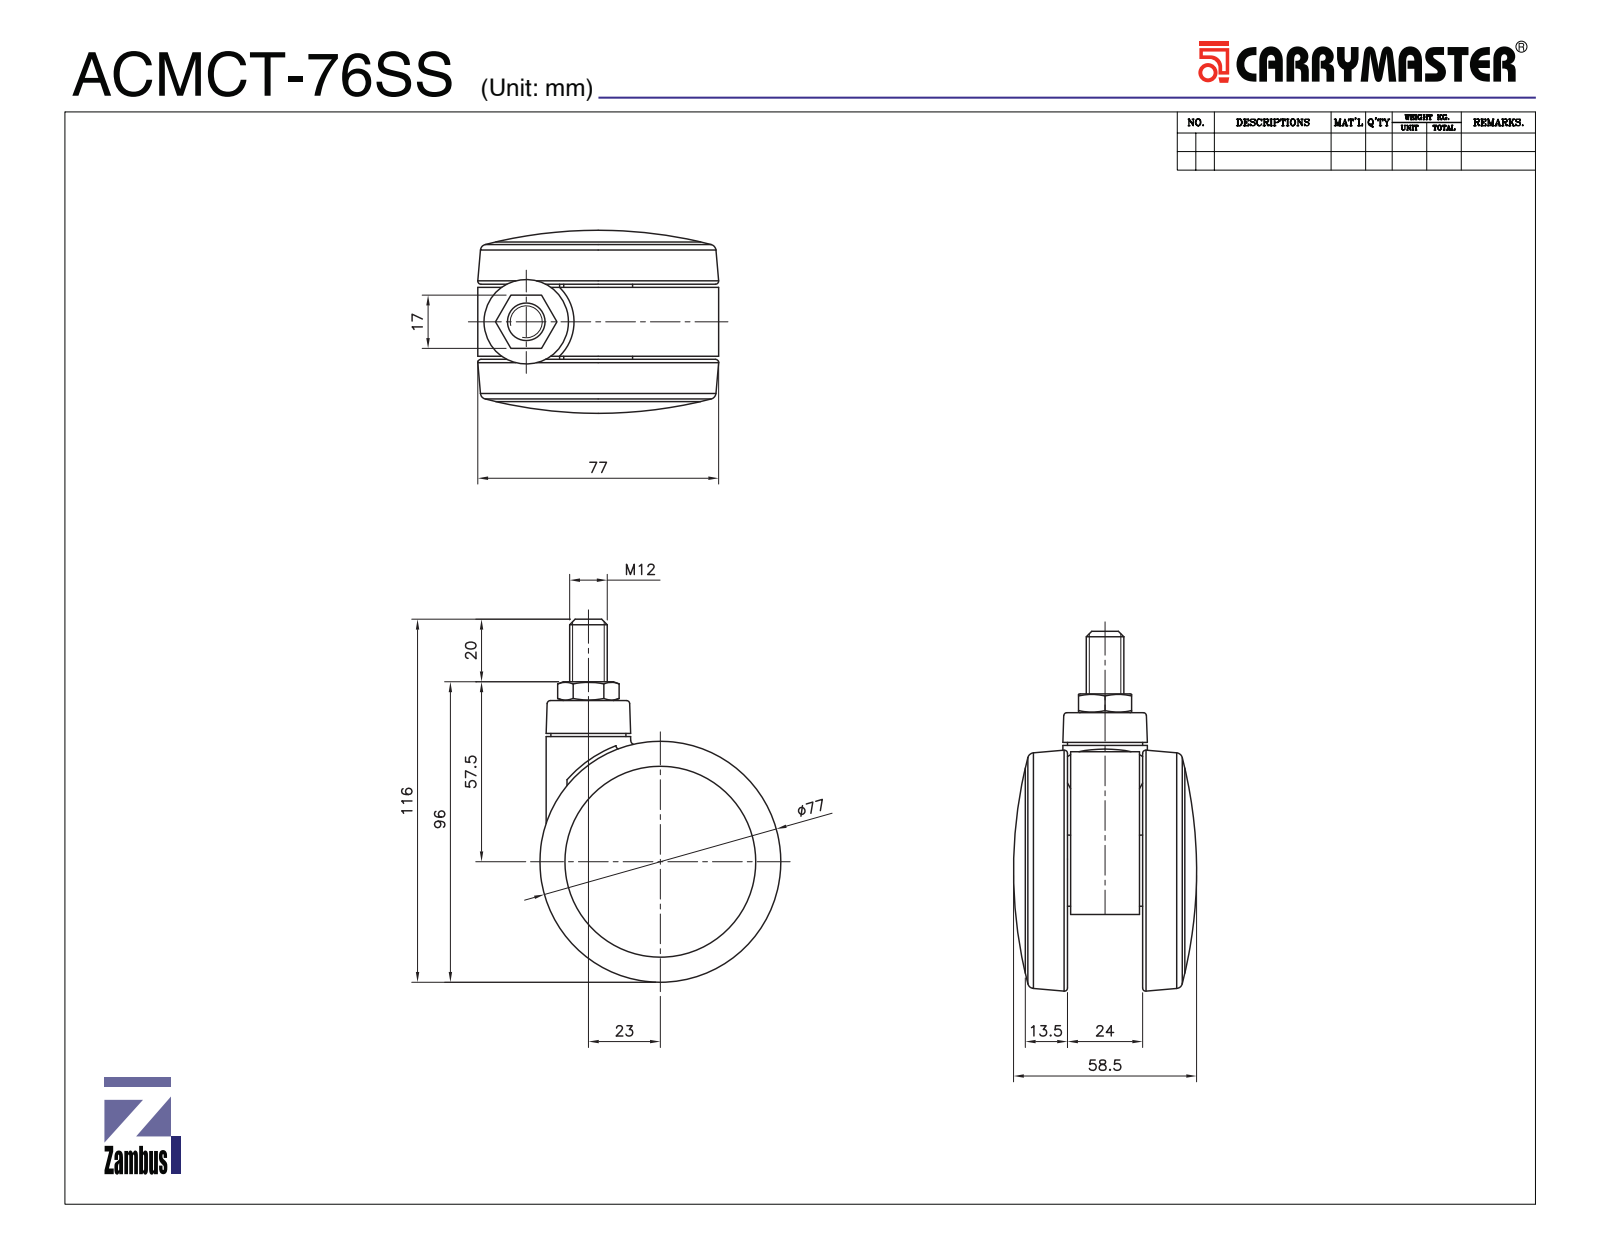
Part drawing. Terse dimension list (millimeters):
name: ACMC-76 WHEEL; 76 NON BRAKE TYPE FRAME; ACMCT-76 SS TYPE TOP PLATE; ACMCT_76SS_3D
written by: SolidWorks 2020 (CONFIG_CONTROL_DESIGN)
unit: mm
bodies: 4 solids, 163 faces (40 planar, 69 cylindrical, 54 other)
size: 115.5 × 77 × 58.5
volume: 164 919 mm³; area: 47 172 mm²
holes: 1× ⌀15, 1× ⌀55, 1× ⌀61.2
bosses: 1× ⌀61, 1× ⌀28, 1× ⌀27, 1× ⌀24, 1× ⌀22, 1× ⌀17, 1× ⌀11, 1× ⌀10.25
rounds: 1× R36, 1× R38.5, 1× R40
face distances: 13.5, 30.5, 17, 44, 1.5, 1, 19.5, 12, 32, 18.5
